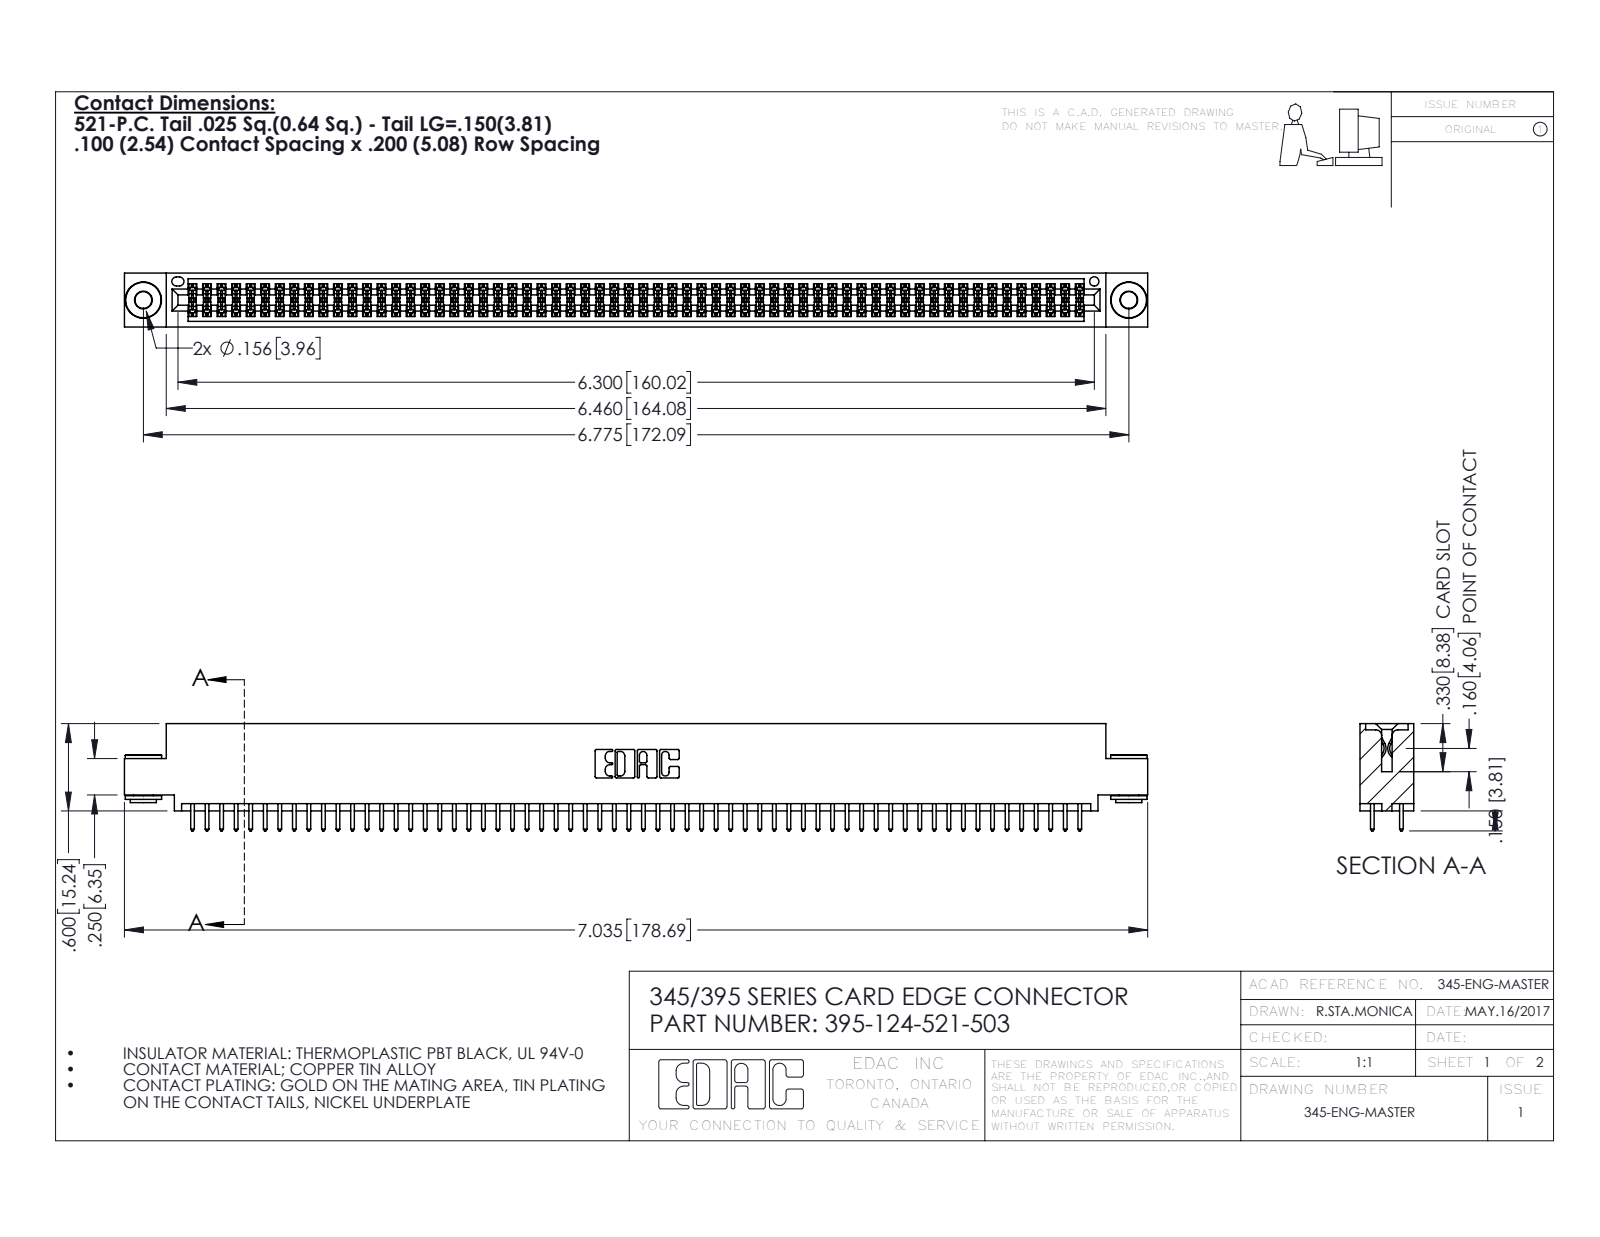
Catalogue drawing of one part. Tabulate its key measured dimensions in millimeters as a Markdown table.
| quantity | value |
| --- | --- |
| part name | 345-250-002_345-250-002-102; 395-124-521-503; 345-292-001_345-293-121; 345 Part_0.110 Offset - 0.156 Dia-TH |
| STEP written by | SolidWorks 2016 (CONFIG_CONTROL_DESIGN) |
| units | millimeters |
| bodies | 127 solids, 6368 faces (4186 planar, 2174 cylindrical, 8 other) |
| overall size | 178.7 × 18.7 × 9.4 |
| volume | 17 440 mm³ |
| surface area | 26 140 mm² |
| round holes (diameter × count) | 2.9 × 2, 4 × 2, 1.6 × 1 |
| round bosses / shafts (diameter × count) | 6.4 × 2, 4.6 × 2, 3.5 × 2 |
| partial cylindrical surfaces (radius × count) | 0.2 × 186, 0.3 × 124, 0.3 × 22, 0.2 × 6, 0.8 × 6, 0.7 × 3, 0.4 × 2, 0.5 × 2 |
| main face-to-face distances | 1.8, 7.6, 5.1, 0.6, 2.5, 6.9, 9.4, 5.7, 4.4, 3.8 |
| hole center spacings | 6.9, 166.1, 172.1 |
